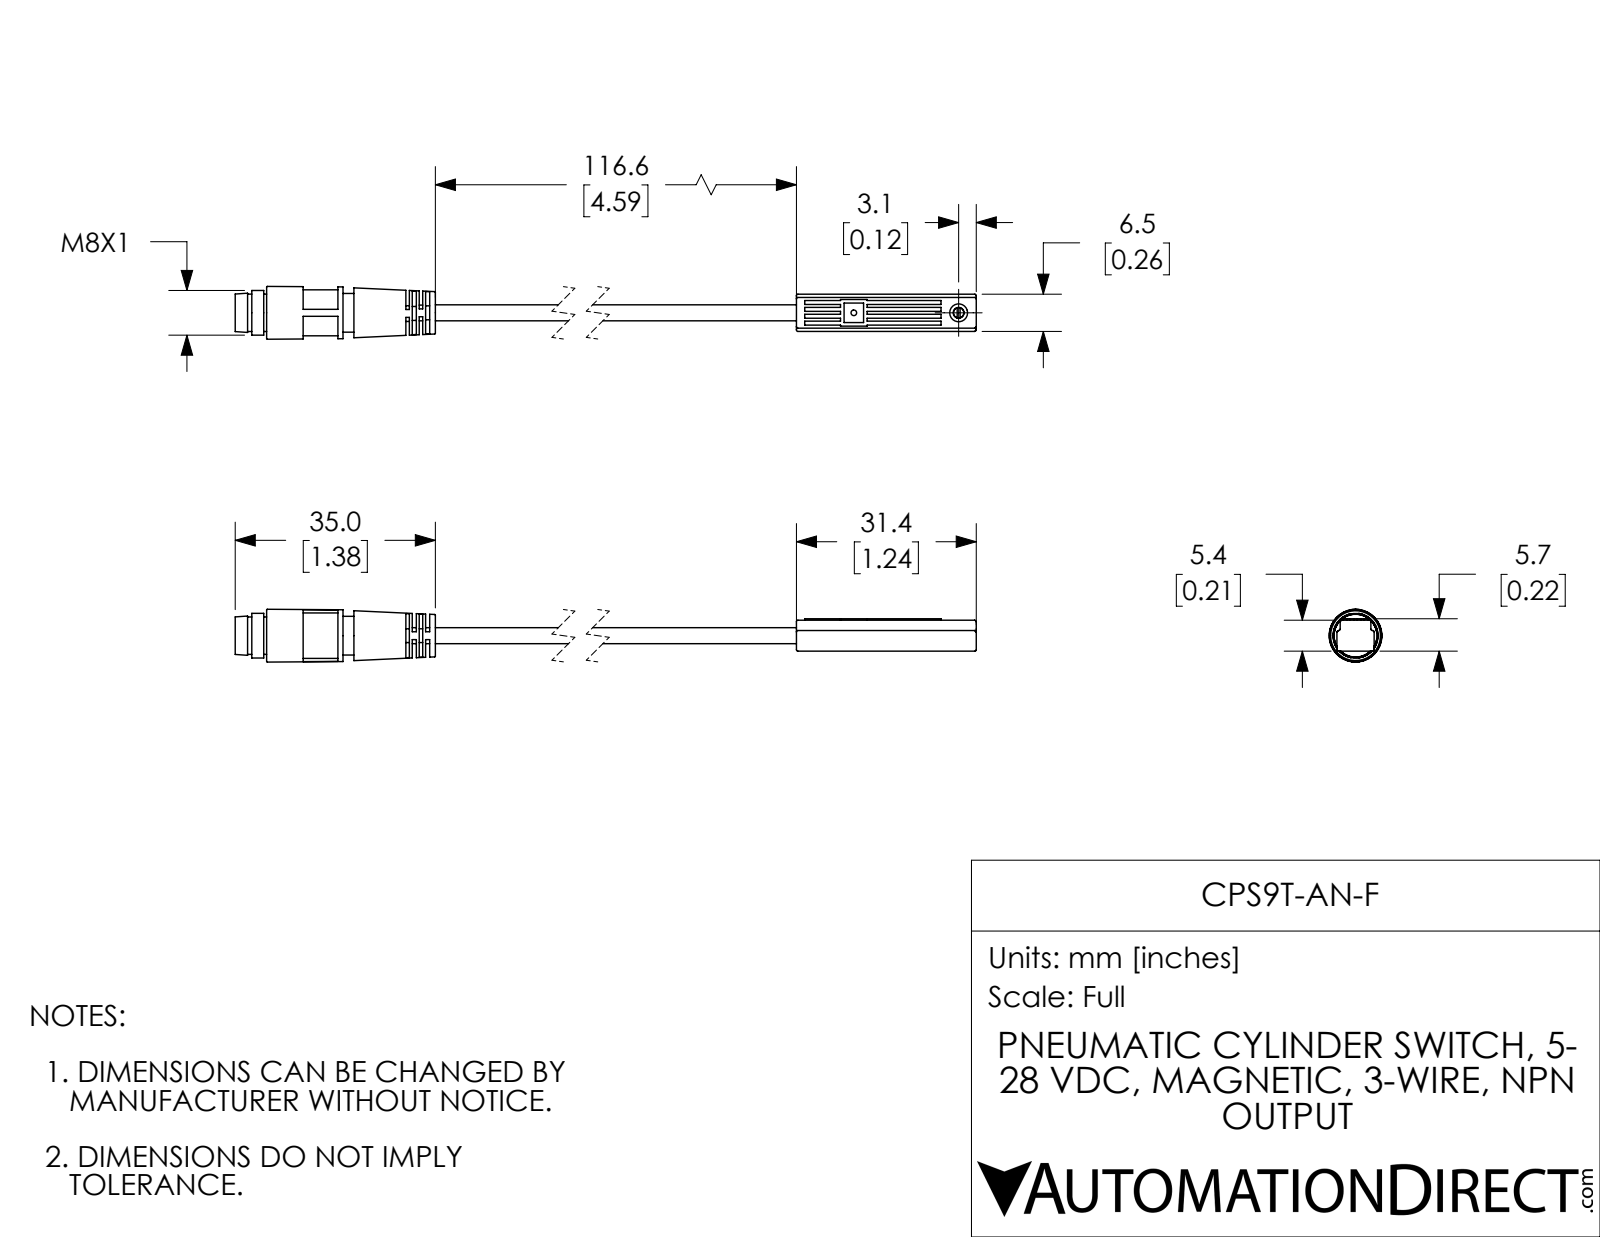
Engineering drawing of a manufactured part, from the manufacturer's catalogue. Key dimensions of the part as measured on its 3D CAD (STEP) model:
Part name (STEP PRODUCT): CPS9T-AN-F
STEP written by: SolidWorks 2017 (AUTOMOTIVE_DESIGN)
Units: inches
Bodies: 2 solids, 227 faces (113 planar, 64 cylindrical, 50 other)
Overall size (bounding box): 7.202 × 0.363 × 0.363
Volume: 0.205 in³ · Surface area: 5.27 in²
Round holes (diameter × count): ⌀0.075 ×1, ⌀0.123 ×1, ⌀0.214 ×1, ⌀0.228 ×1
Round bosses / shafts (diameter × count): ⌀0.039 ×3, ⌀0.316 ×1, ⌀0.307 ×1, ⌀0.266 ×1, ⌀0.257 ×1, ⌀0.11 ×1, ⌀0.071 ×1
Partial cylindrical surfaces — rounded edges, fillets, slot ends (radius × count): R0.01 ×22, R0.054 ×2, R0.055 ×1
Main face-to-face distances: 0.092, 0.02, 0.048, 0.044, 0.072, 0.256, 0.024, 0.022, 0.233, 0.213
